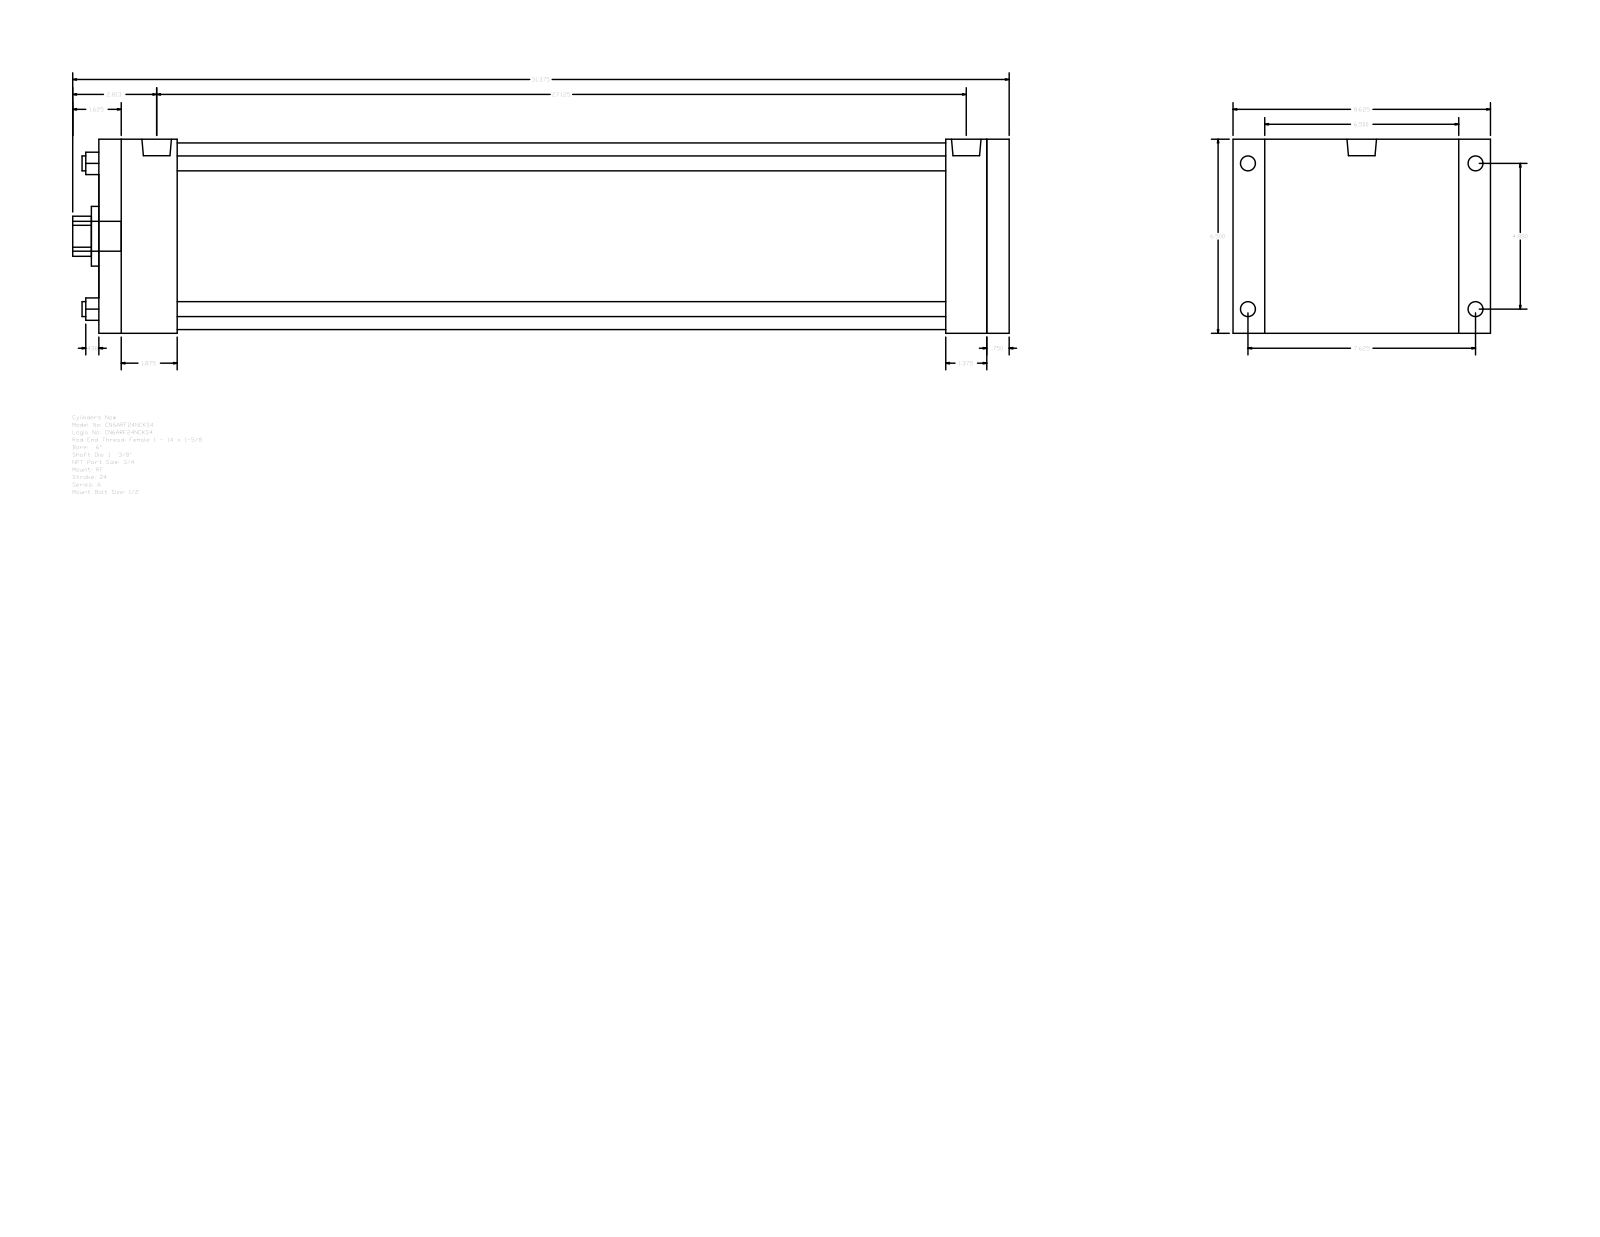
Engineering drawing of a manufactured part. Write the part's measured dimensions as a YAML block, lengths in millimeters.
part_name: "A_RF__0600_1.375"
step_written_by: "GSSL Pune (CONFIG_CONTROL_DESIGN)"
units: millimeters
bodies: {solids: 0, faces: 92, planar: 64, cylindrical: 28, other: 0}
overall_size: [796.92, 219.07, 165.1]
round_holes:
  - {diameter: 12.7, count: 4}
  - {diameter: 34.92, count: 1}
  - {diameter: 50.8, count: 1}
  - {diameter: 158.75, count: 1}
round_bosses_or_shafts:
  - {diameter: 15.08, count: 4}
  - {diameter: 12.7, count: 4}
  - {diameter: 25.12, count: 2}
  - {diameter: 25.4, count: 1}
partial_cylinders:
  - {radius: 17.06, count: 1}
face_to_face_distances: [165.1, 774.69, 19.04, 755.65, 66.67, 688.98, 708.02, 720.72, 654.05, 34.93]
hole_center_spacings: [87.65, 123.96, 175.31]
